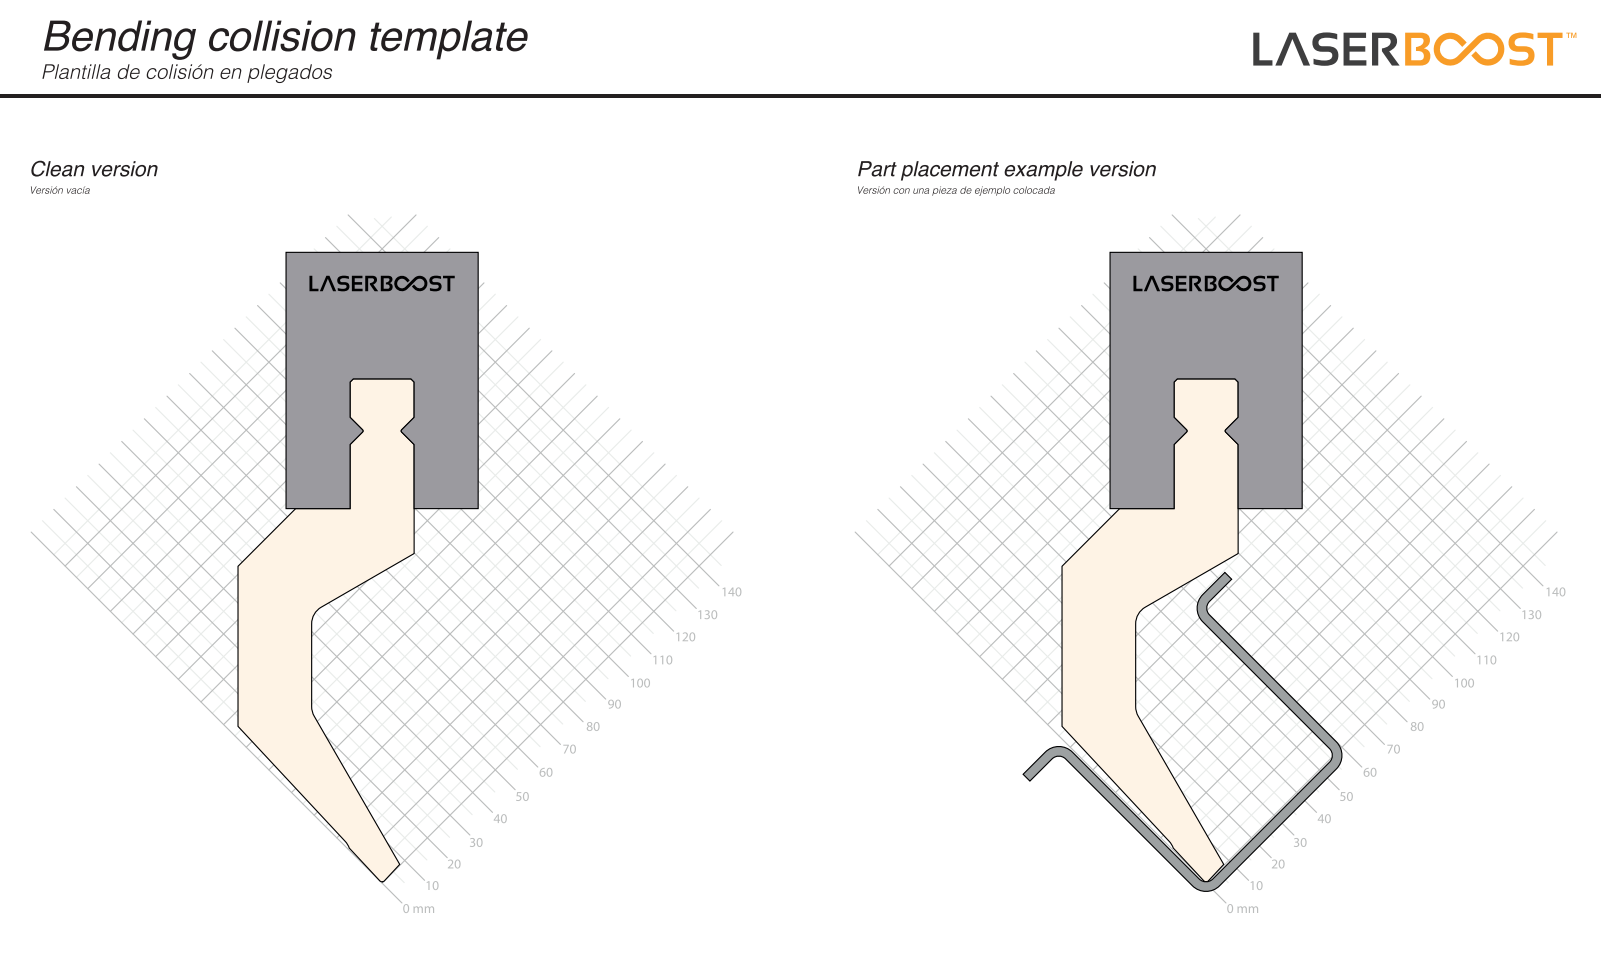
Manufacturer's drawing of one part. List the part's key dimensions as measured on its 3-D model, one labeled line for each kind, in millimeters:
Part name (STEP PRODUCT): EXTENSOR_80_AF0; OW202K_AF0; PRT0001; EXTENSORWEB_ASM (+4 more)
STEP written by: PRO/ENGINEER BY PARAMETRIC TECHNOLOGY CORPORATION, 2012130 (CONFIG_CONTROL_DESIGN)
Units: millimetres
Bodies: 5 solids, 368 faces (220 planar, 8 cylindrical, 140 other)
Overall size (bounding box): 387.03 × 240.03 × 100
Volume: 1 771 000 mm³ · Surface area: 251 215 mm²
Partial cylindrical surfaces — rounded edges, fillets, slot ends (radius × count): R3 ×4, R6 ×4
Main face-to-face distances: 3, 100, 300, 59.99, 55, 219.3, 35, 20, 56.99, 62.99
